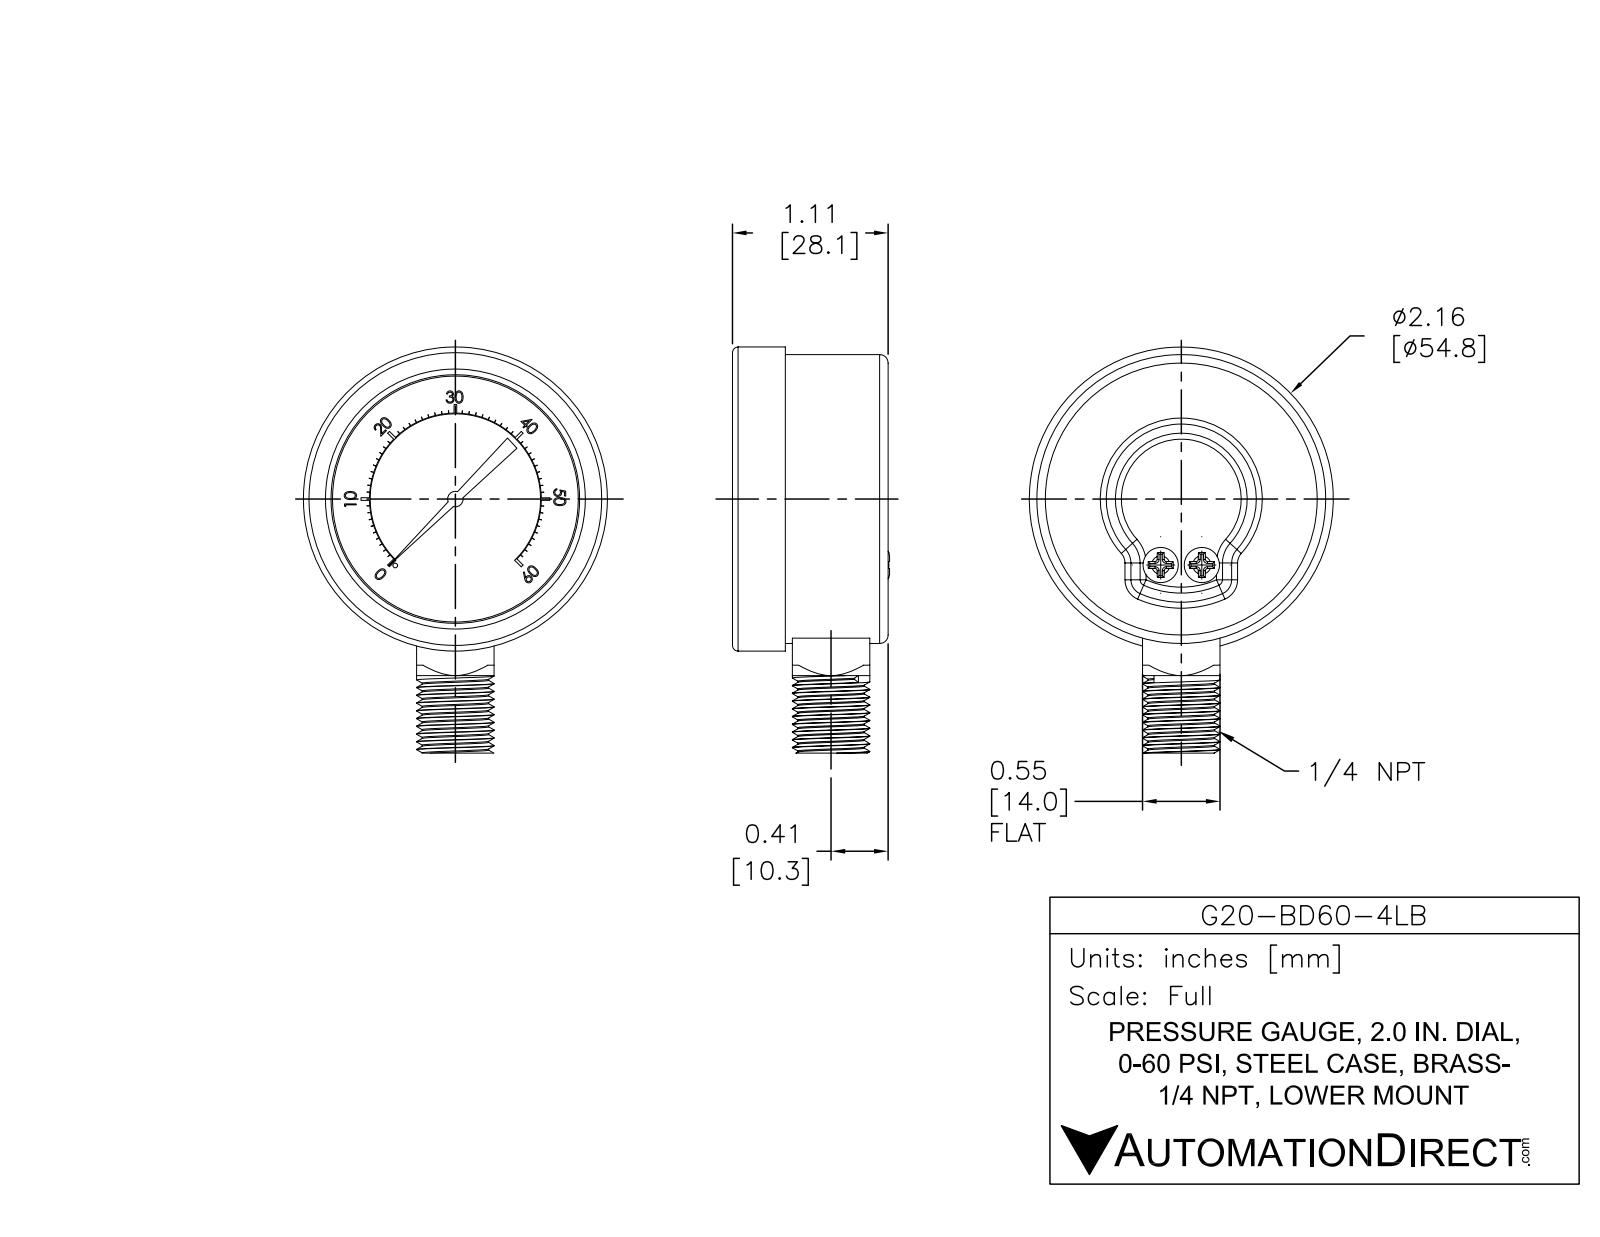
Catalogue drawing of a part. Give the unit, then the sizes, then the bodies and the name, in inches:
Units: inches
Overall size (bounding box): 2.882 × 2.158 × 1.115
Round holes (diameter × count): ⌀0.14 ×1, ⌀1.745 ×1
Round bosses / shafts (diameter × count): ⌀0.25 ×2, ⌀2.158 ×1, ⌀2.05 ×1, ⌀0.55 ×1, ⌀0.11 ×1, ⌀0.033 ×1
Partial cylindrical surfaces — rounded edges, fillets, slot ends (radius × count): R0.06 ×4, R0.605 ×1, R0.61 ×1
Main face-to-face distances: 0.815, 1.105, 0.29, 0.1, 0.715, 1.005, 0.63, 0.73, 0.085, 0.375
Volume: 3.182 in³ · Surface area: 18.02 in²
Bodies: 1 solid, 416 faces (270 planar, 81 cylindrical, 65 other)
Part name (STEP PRODUCT): G20-BD60-4LB
STEP written by: SolidWorks 2021 (AUTOMOTIVE_DESIGN)
